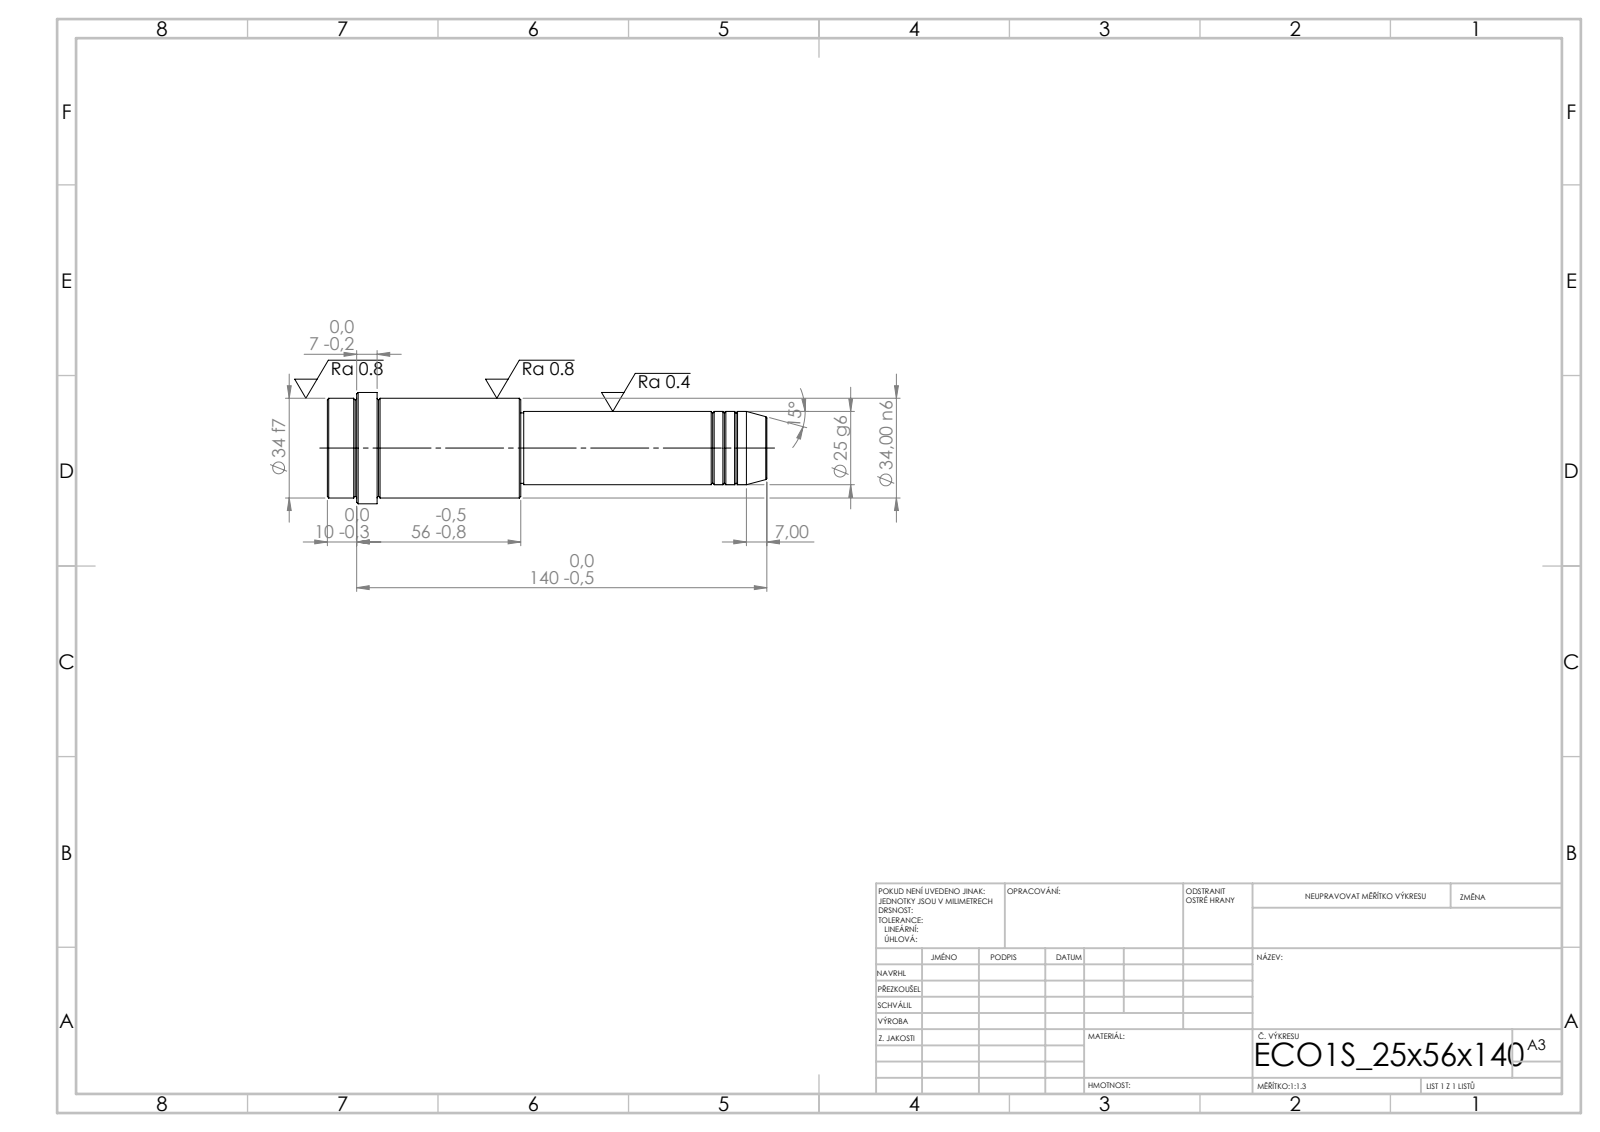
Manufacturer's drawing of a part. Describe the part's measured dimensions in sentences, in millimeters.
Its 3-D file was written by "SolidWorks 2019 (CONFIG_CONTROL_DESIGN)". It is 1 solid with 52 faces: 6 planar, 16 cylindrical and 30 other. Overall it measures 150 by 38 by 38 millimeters. Its volume is 101 994 cubic millimeters and its surface area 16 052 square millimeters. Round bosses or shafts: 1 of diameter 38, 1 of diameter 34, 1 of diameter 25, 1 of diameter 24. The main face-to-face distances are 66, 84, 150, 133, 49, 17, 140, 56, 7, 10.
